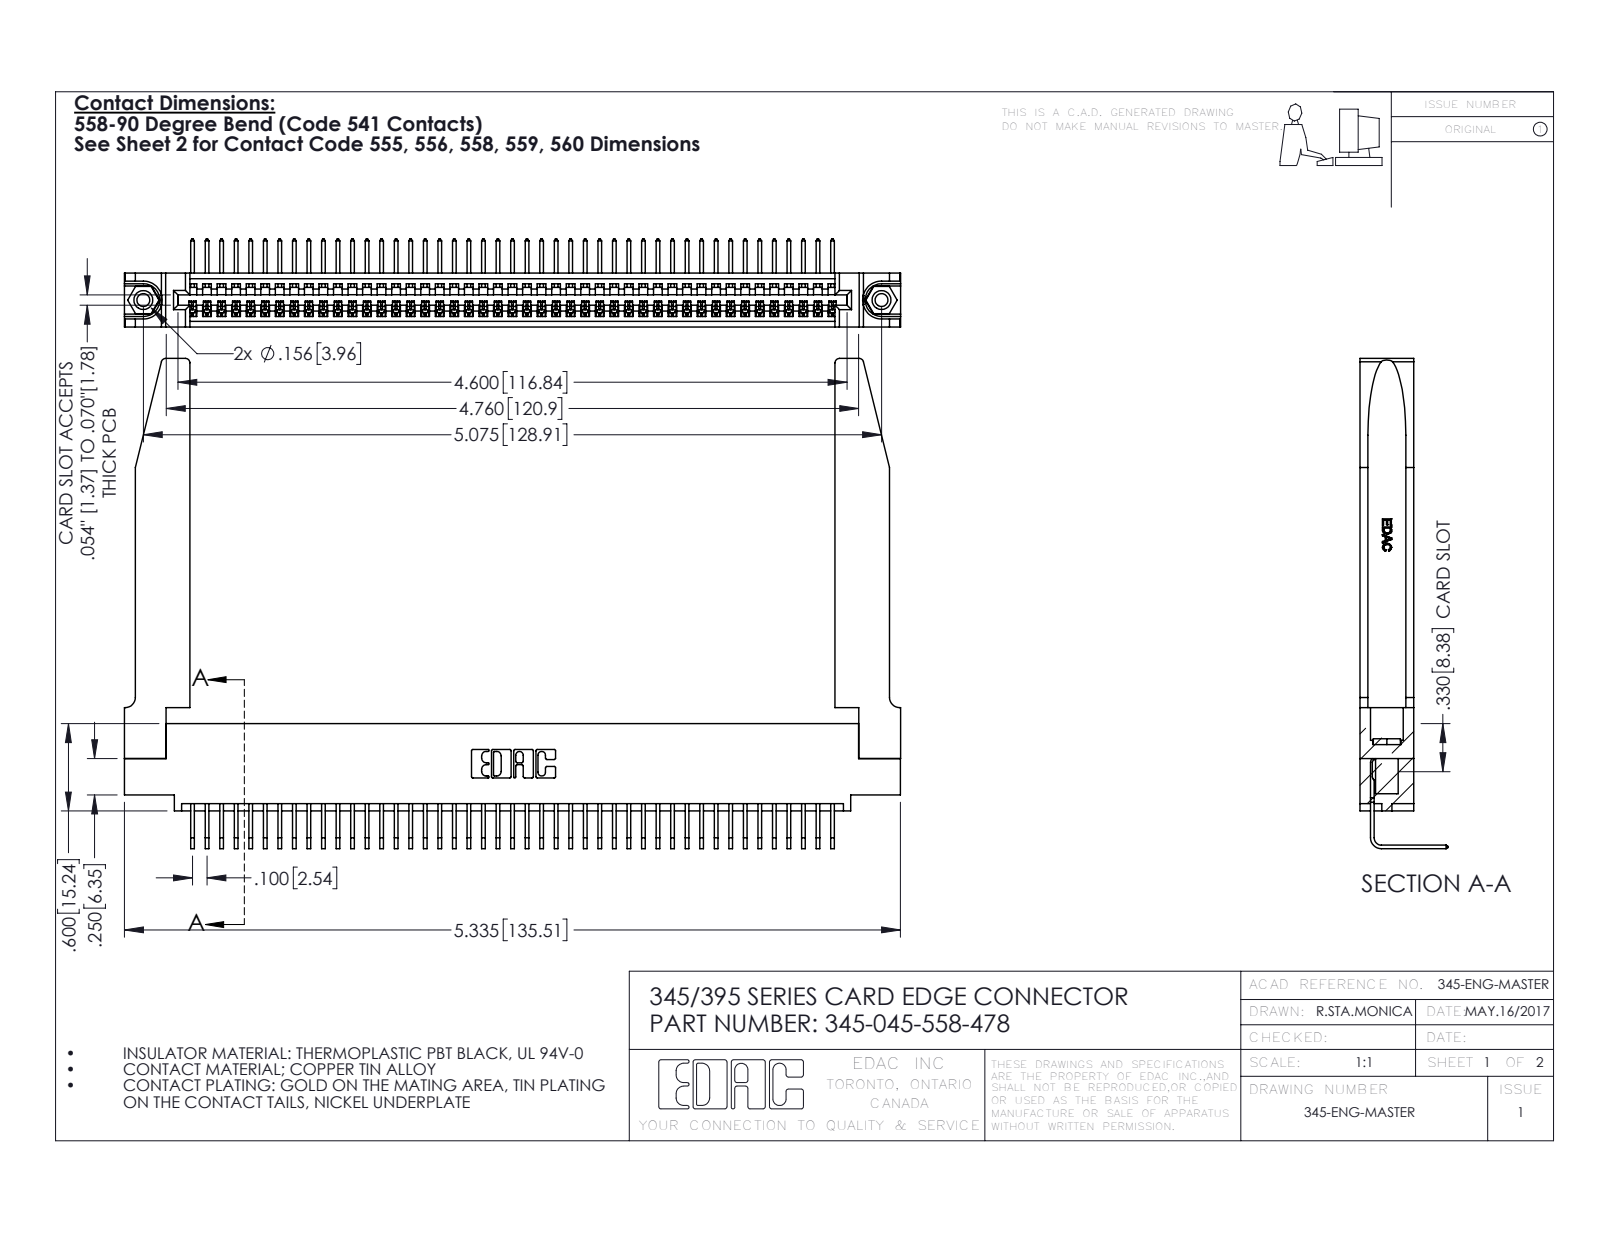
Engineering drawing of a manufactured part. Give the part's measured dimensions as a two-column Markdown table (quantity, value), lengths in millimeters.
| quantity | value |
| --- | --- |
| part name | 345-292-001_558 Tail - 2; 345-220-078_345-220-078; 345-045-558-478; 345-250-001_345-250-001-102 (+1 more) |
| STEP written by | SolidWorks 2016 (CONFIG_CONTROL_DESIGN) |
| units | millimeters |
| bodies | 50 solids, 3064 faces (2116 planar, 896 cylindrical, 52 other) |
| overall size | 135.5 × 85.6 × 15.4 |
| volume | 20 750 mm³ |
| surface area | 25 090 mm² |
| round holes (diameter × count) | 2.3 × 2, 3.2 × 2, 4 × 2, 1.6 × 1 |
| round bosses / shafts (diameter × count) | 3.9 × 2 |
| partial cylindrical surfaces (radius × count) | 0.2 × 90, 0.3 × 22, 0.8 × 8, 0.2 × 6, 0.8 × 6, 0.7 × 3, 0.8 × 2, 1 × 2 |
| main face-to-face distances | 9.4, 1.8, 7.6, 5.1, 2.5, 6.9, 0.6, 5.7, 3.8, 3.8 |
| hole center spacings | 6.9, 122.9, 128.9 |
